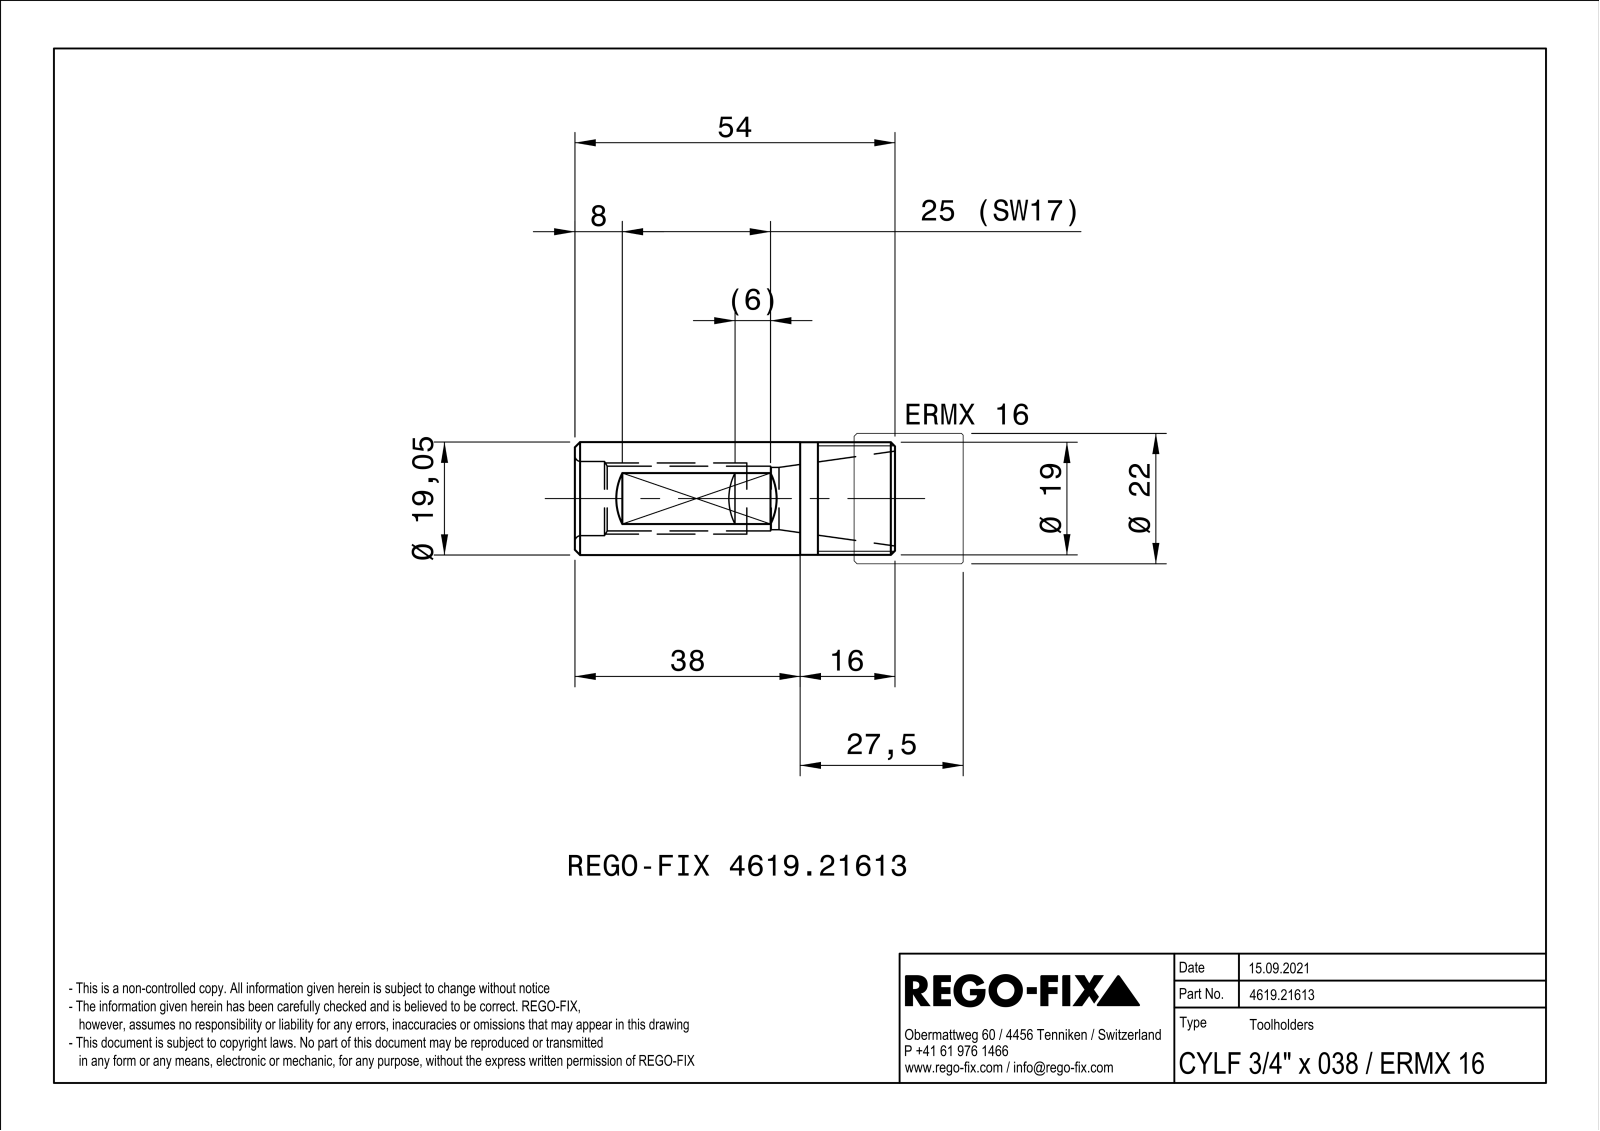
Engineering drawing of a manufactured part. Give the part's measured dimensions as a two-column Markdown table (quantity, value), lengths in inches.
| quantity | value |
| --- | --- |
| part name | NOCUT |
| STEP written by | SIEMENS PLM Software Solid Edge ST10 (AUTOMOTIVE_DESIGN) |
| units | inches |
| bodies | 2 solids, 43 faces (17 planar, 12 cylindrical, 14 other) |
| overall size | 2.134 × 0.76 × 0.76 |
| volume | 1.135 in³ |
| surface area | 16.98 in² |
| round holes (diameter × count) | 0.413 × 1, 0.43 × 1, 0.492 × 1 |
| round bosses / shafts (diameter × count) | 0.76 × 1, 0.75 × 1, 0.748 × 1 |
| main face-to-face distances | 0.669, 2.134, 2.126, 0.222, 0.306, 0.638, 0.63, 1.496 |
